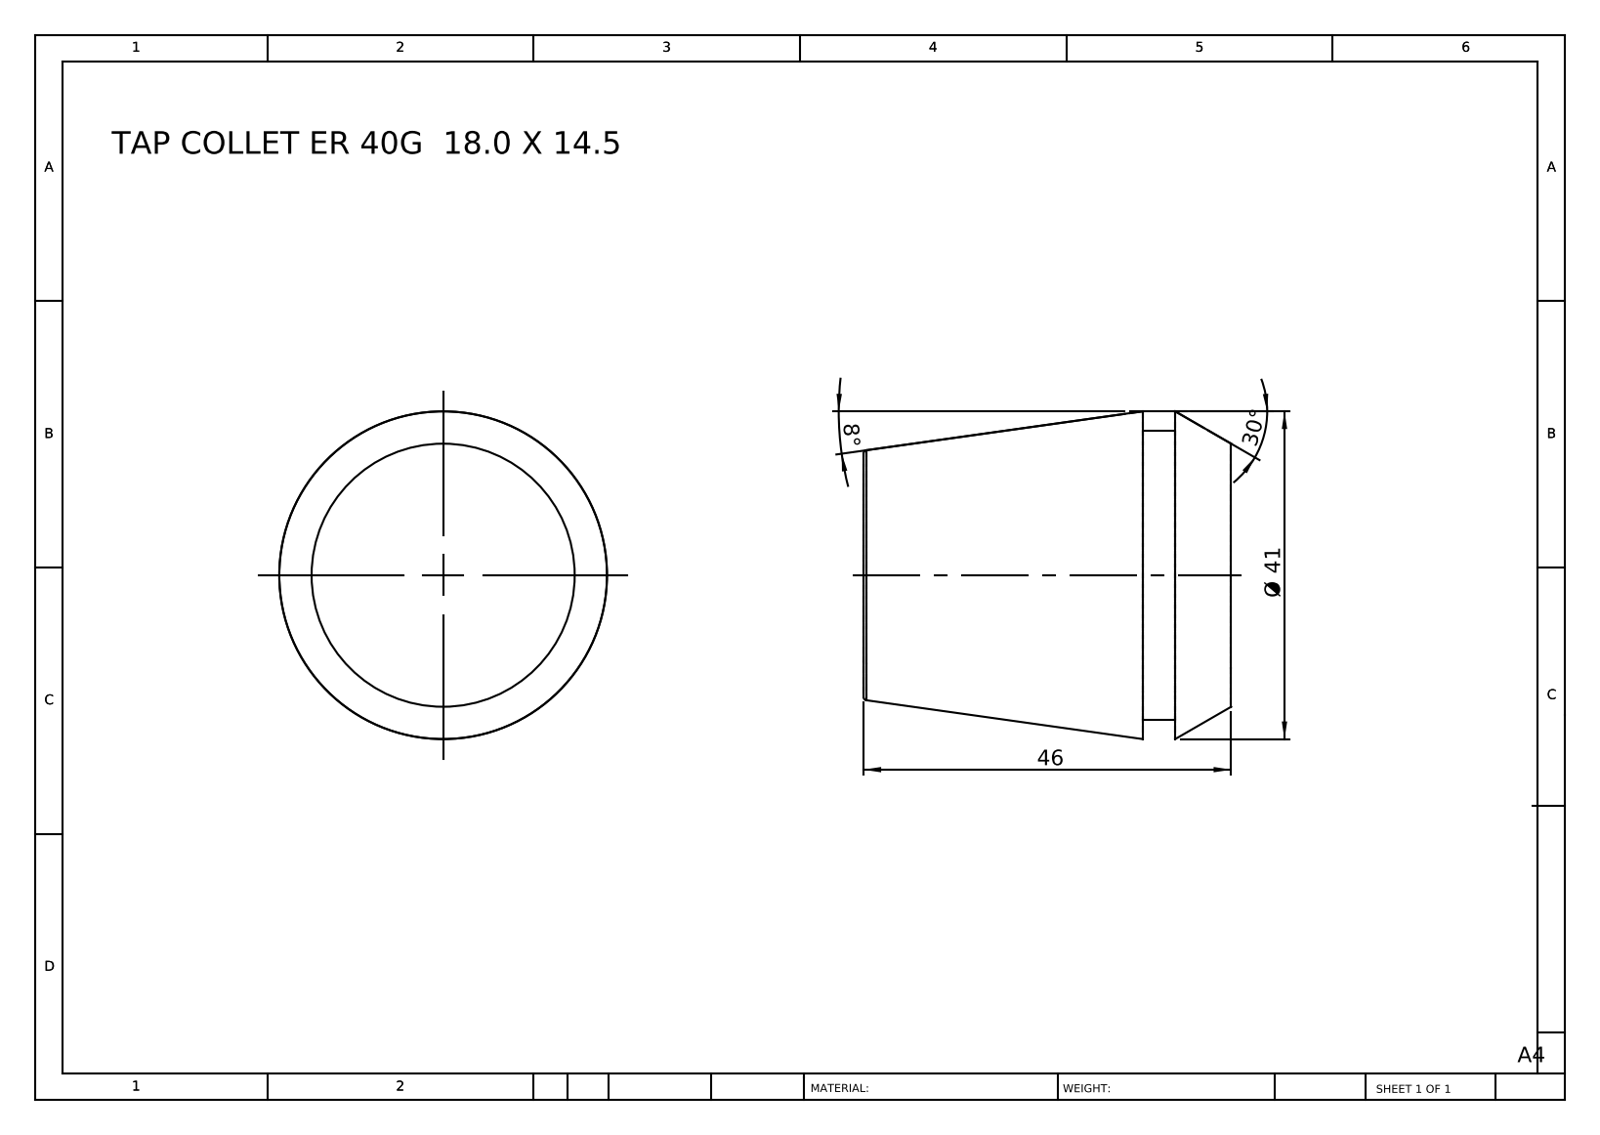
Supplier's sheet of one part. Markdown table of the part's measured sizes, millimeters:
| quantity | value |
| --- | --- |
| part name | TAP COLLET ER 40G 18.0 X 14.5 |
| STEP written by | SolidWorks 2014 (CONFIG_CONTROL_DESIGN) |
| units | millimeters |
| bodies | 1 solid, 12 faces (4 planar, 2 cylindrical, 6 other) |
| overall size | 46 × 41 × 41 |
| volume | 47 690 mm³ |
| surface area | 7 586 mm² |
| round bosses / shafts (diameter × count) | 36.2 × 1 |
| main face-to-face distances | 46, 11.1, 34.9, 7, 4.1, 39 |
